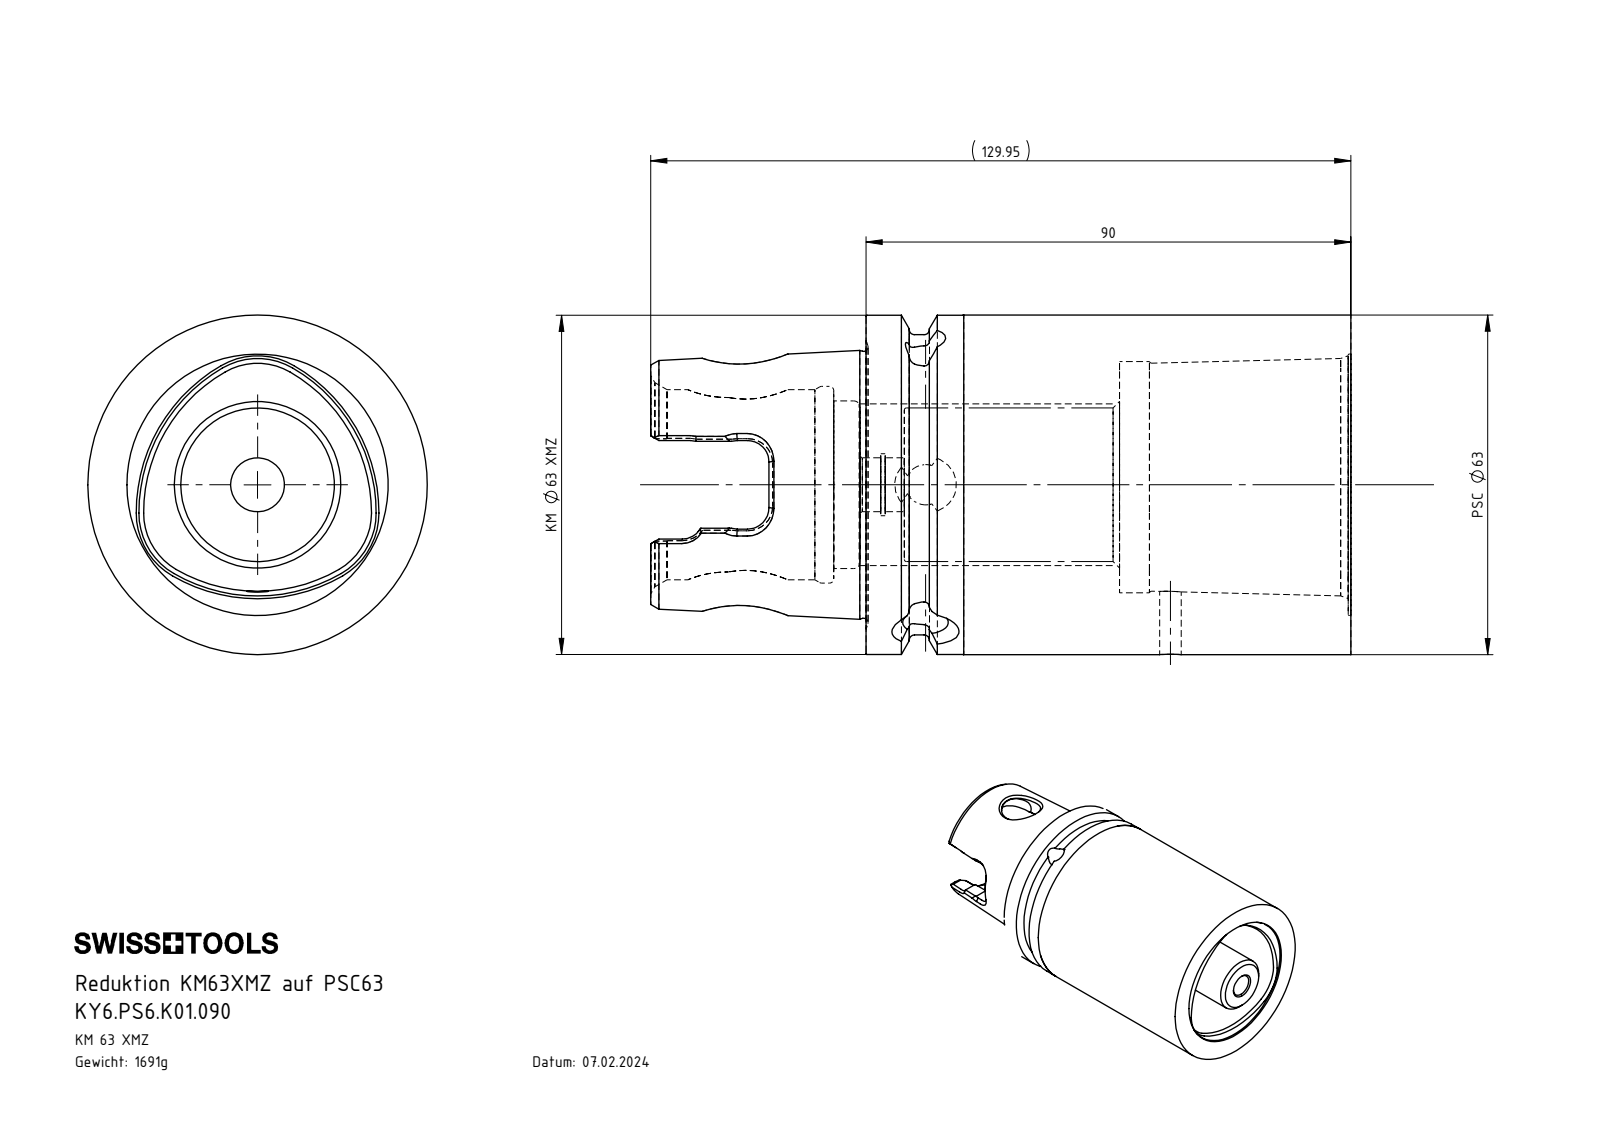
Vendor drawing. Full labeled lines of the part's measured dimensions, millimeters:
Part name (STEP PRODUCT): KY6.PS6.K01.090; PS6-ER2.001.024_A; PS6-ER1.K01.071_A_PreviewCfg; KY6-PS6.K01.090_A
STEP written by: SolidWorks 2022 (AUTOMOTIVE_DESIGN)
Units: millimetres
Bodies: 3 solids, 314 faces (60 planar, 89 cylindrical, 165 other)
Overall size (bounding box): 133.55 × 63 × 63
Volume: 249 763 mm³ · Surface area: 57 198 mm²
Round holes (diameter × count): ⌀7.47 ×2, ⌀4 ×1, ⌀8 ×1, ⌀8.48 ×1, ⌀10 ×1, ⌀11.5 ×1, ⌀14.5 ×1, ⌀20.4 ×1, ⌀28.5 ×1, ⌀31.1 ×1, ⌀35.27 ×1, ⌀36.5 ×1
Round bosses / shafts (diameter × count): ⌀63 ×1, ⌀62.95 ×1, ⌀55.7 ×1, ⌀31.4 ×1, ⌀30 ×1, ⌀27.6 ×1, ⌀27.5 ×1, ⌀20 ×1
Partial cylindrical surfaces — rounded edges, fillets, slot ends (radius × count): R2.3 ×6, R4 ×6, R6 ×6, R12.4 ×3, R30.5 ×3, R7.04 ×2
Main face-to-face distances: 82.9, 39.95, 47.05, 7.1, 90, 42.95, 8.2, 1.1, 48.15, 91.1
Hole centre spacings: 78.9
